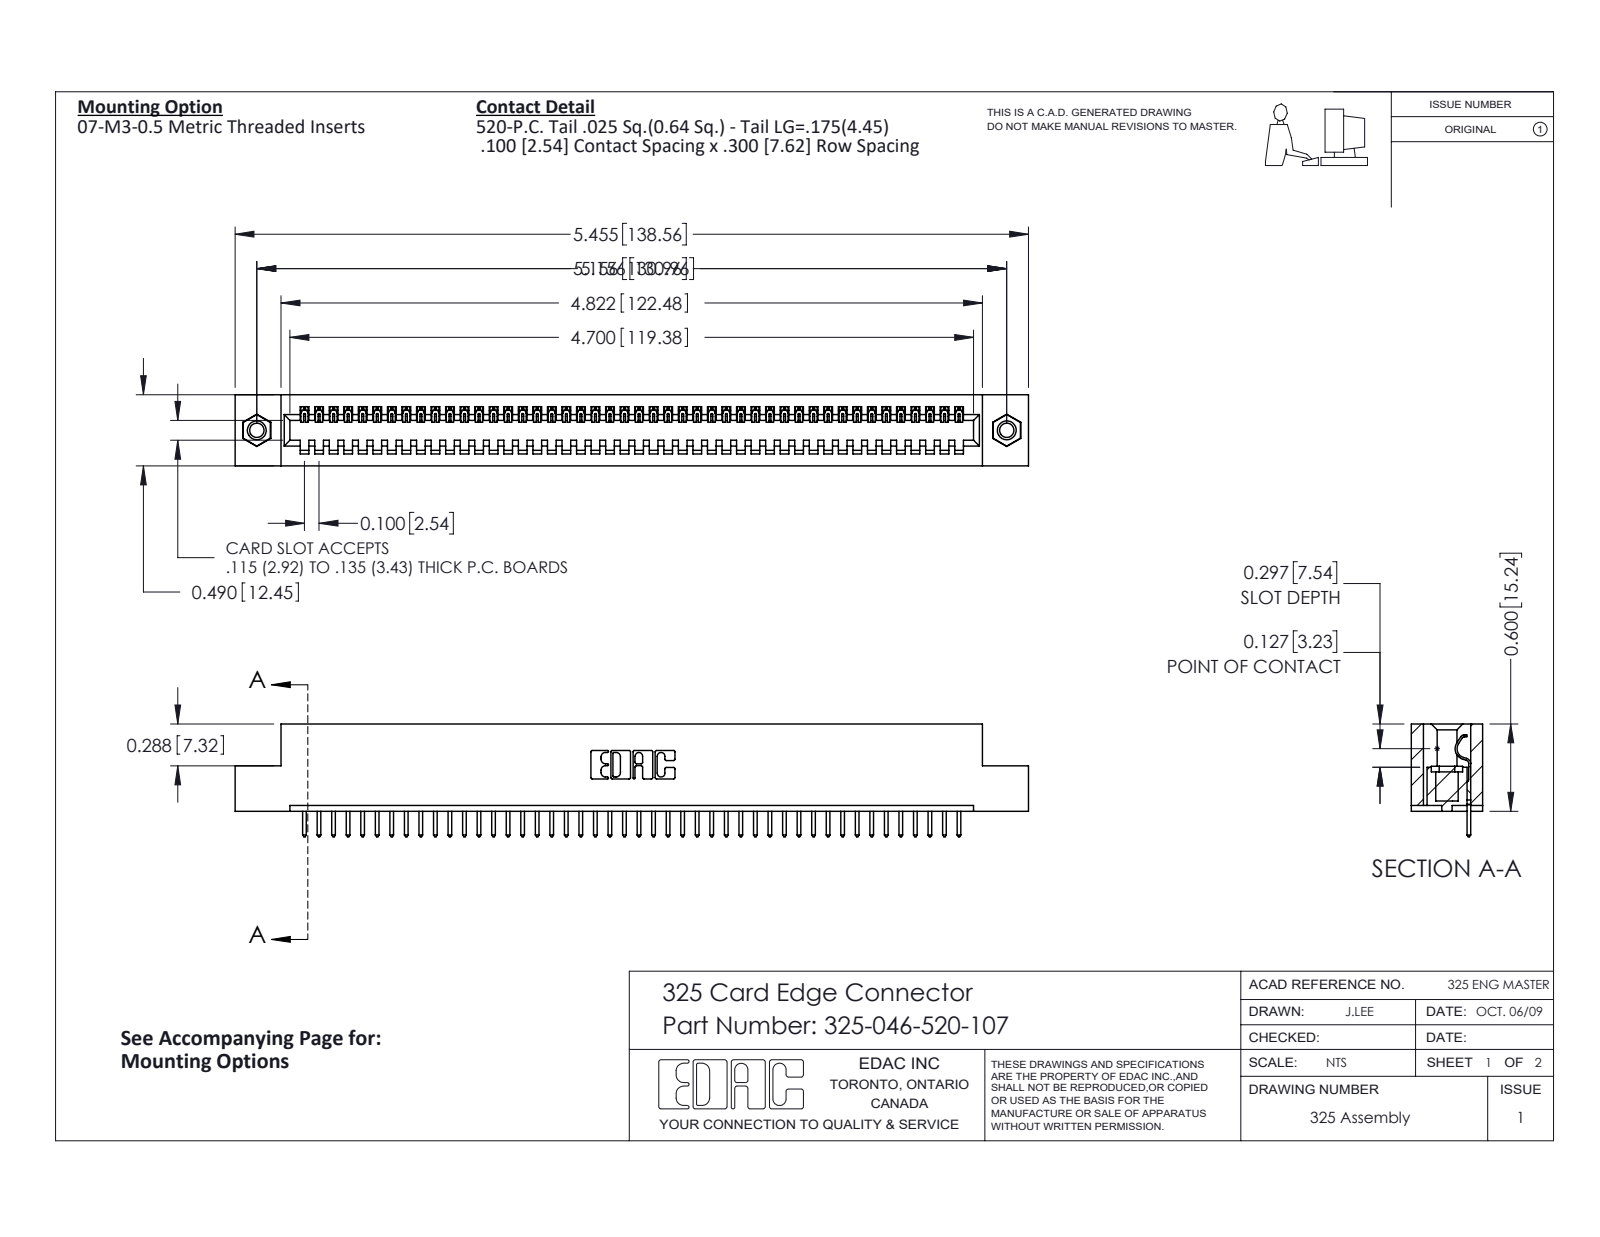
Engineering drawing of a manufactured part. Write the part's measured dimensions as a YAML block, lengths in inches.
part_name: "325-046-520-107; 325 Part_TI; 325-292-001_325-293-120; 345-250-001_345-250-005-103"
step_written_by: "SolidWorks 2016 (CONFIG_CONTROL_DESIGN)"
units: inches
bodies: {solids: 49, faces: 2842, planar: 2034, cylindrical: 792, other: 16}
overall_size: [5.455, 0.775, 0.49]
volume: 1.067
surface_area: 29.01
round_holes:
  - {diameter: 0.098, count: 2}
  - {diameter: 0.125, count: 2}
  - {diameter: 0.16, count: 2}
round_bosses_or_shafts:
  - {diameter: 0.155, count: 2}
partial_cylinders:
  - {radius: 0.006, count: 92}
  - {radius: 0.01, count: 92}
  - {radius: 0.01, count: 22}
  - {radius: 0.007, count: 6}
  - {radius: 0.031, count: 6}
  - {radius: 0.026, count: 3}
  - {radius: 0.014, count: 1}
  - {radius: 0.022, count: 1}
face_to_face_distances: [0.083, 0.407, 0.49, 0.3, 0.107, 0.383, 0.025, 0.325, 0.56, 0.263]
hole_center_spacings: [5.156]
